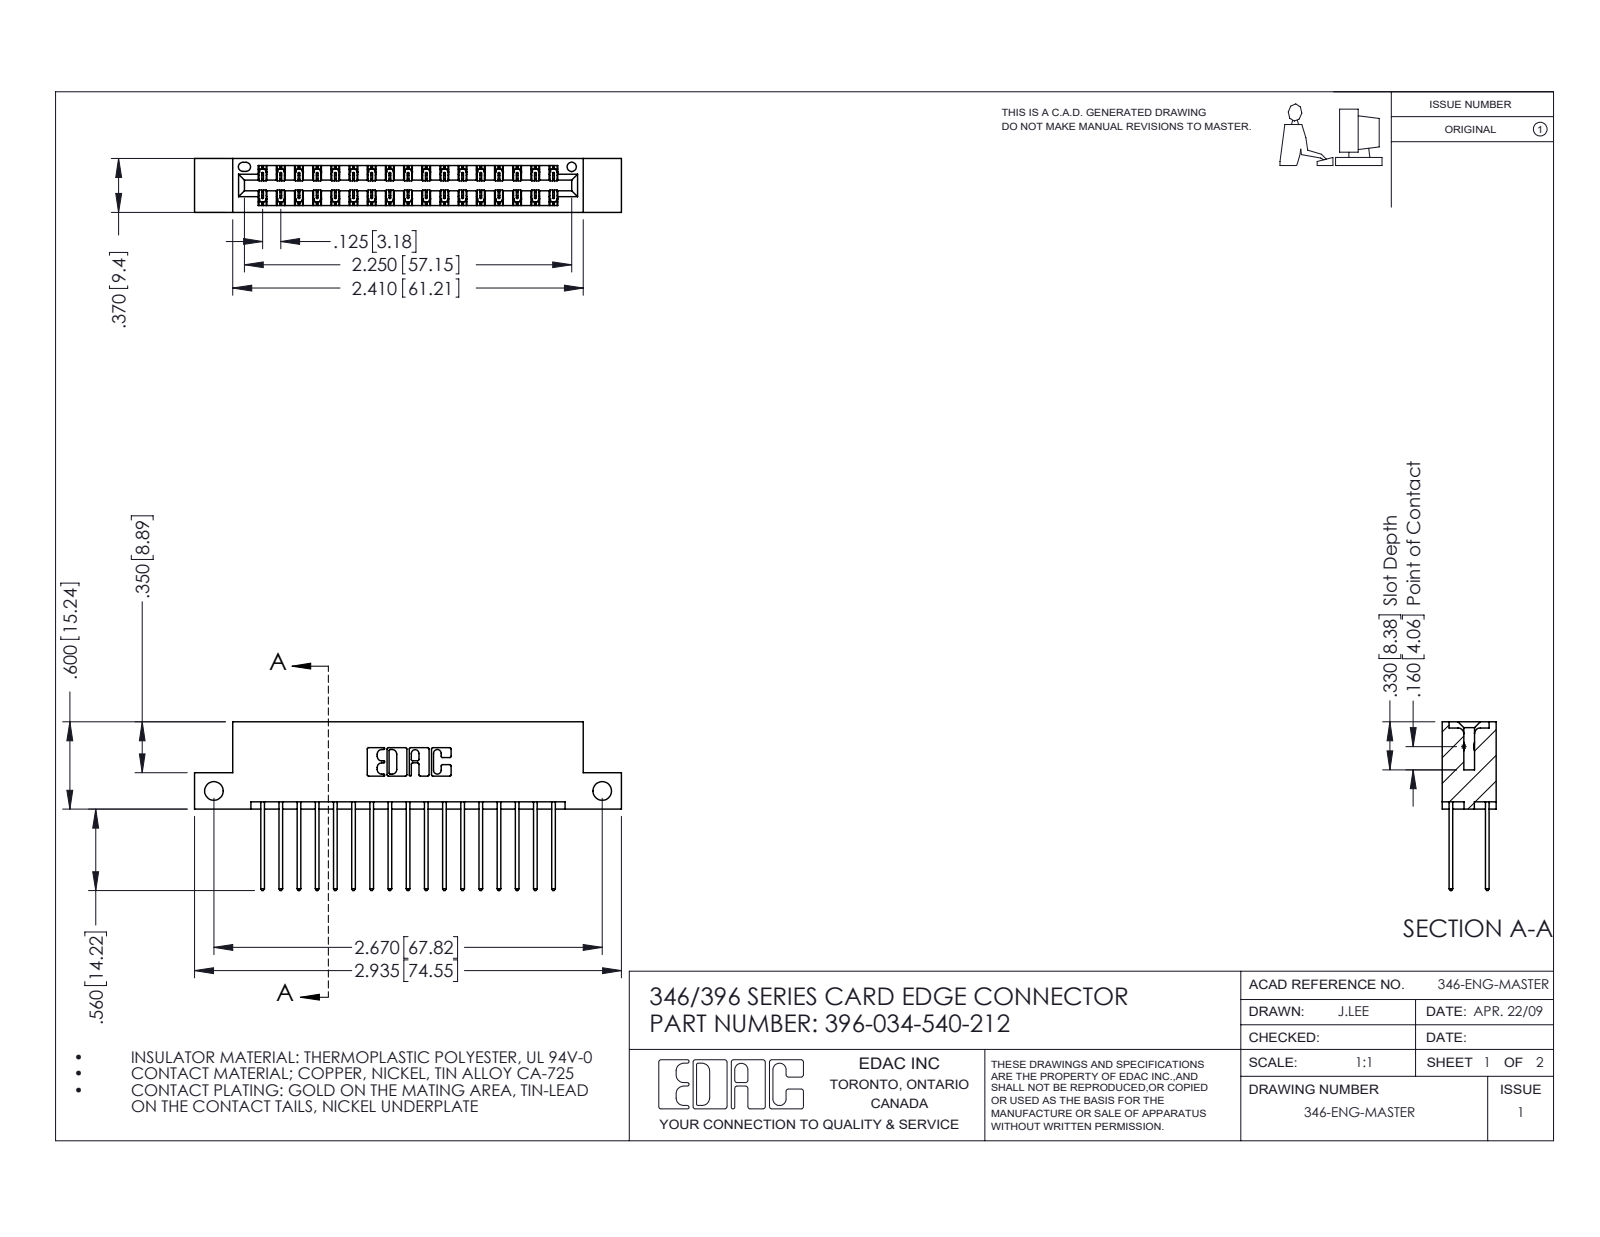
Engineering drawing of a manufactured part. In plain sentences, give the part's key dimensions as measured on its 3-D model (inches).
The part is named "396-034-540-212; 346 Part_Flush Mounting Lugs - Side Mount; 345-292-001_345-293-140". Its 3-D file was written by "SolidWorks 2016 (CONFIG_CONTROL_DESIGN)". It is 35 solids with 1890 faces: 1266 planar, 624 cylindrical and 0 other. Overall it measures 2.935 by 1.16 by 0.37 inches. Its volume is 0.434 cubic inches and its surface area 15.29 square inches. Round holes: 2 of diameter 0.128, 1 of diameter 0.064. Partial cylindrical surfaces (rounded edges, fillets, slot ends): 51 of radius 0.006, 34 of radius 0.01, 22 of radius 0.01, 6 of radius 0.007, 6 of radius 0.031, 3 of radius 0.026, 2 of radius 0.014, 2 of radius 0.022. The main face-to-face distances are 0.048, 0.322, 0.25, 0.37, 0.072, 0.298, 0.025, 0.275, 0.148, 0.222. The hole center spacings are 2.67.
